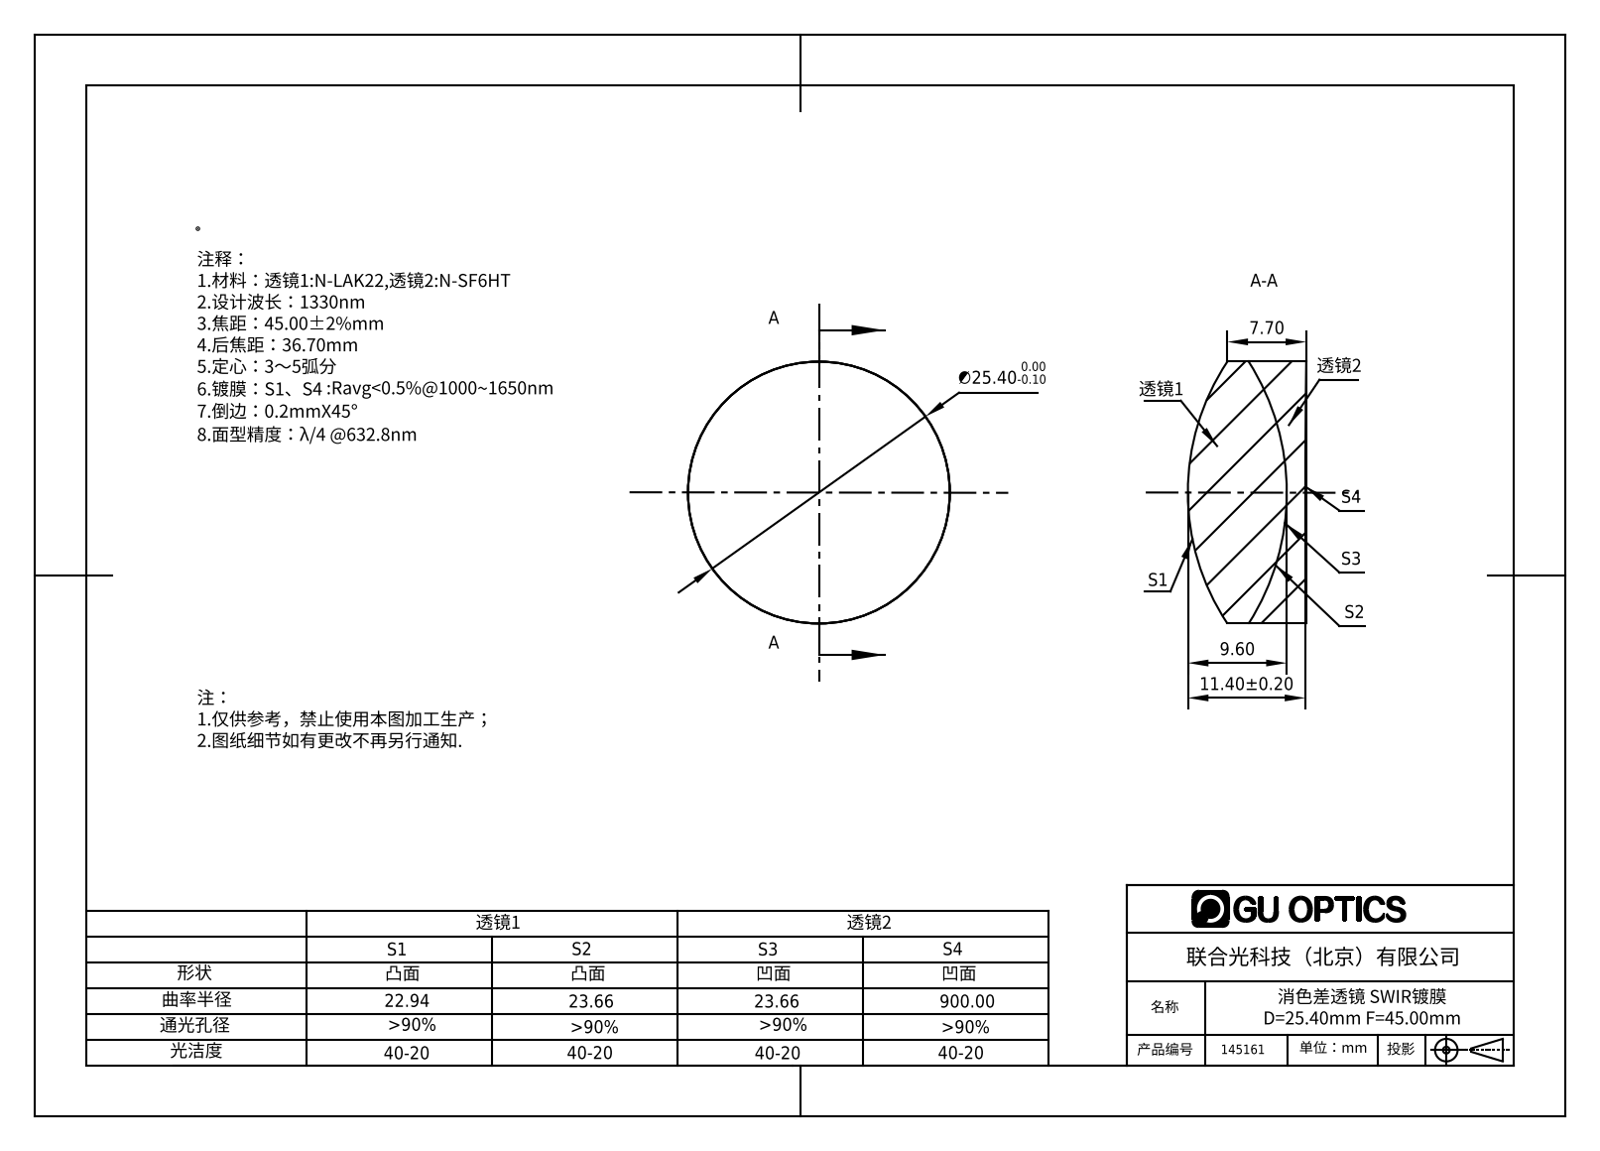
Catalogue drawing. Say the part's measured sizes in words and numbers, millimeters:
The part is named "145161". Its 3-D file was written by "SolidWorks 2016 (AUTOMOTIVE_DESIGN)". It is 2 solids with 12 faces: 0 planar, 4 cylindrical and 8 other. Overall it measures 25.4 by 25.4 by 11.49 millimeters. Its volume is 4 857 cubic millimeters and its surface area 2 770 square millimeters. Round bosses or shafts: 1 of diameter 25.4.
